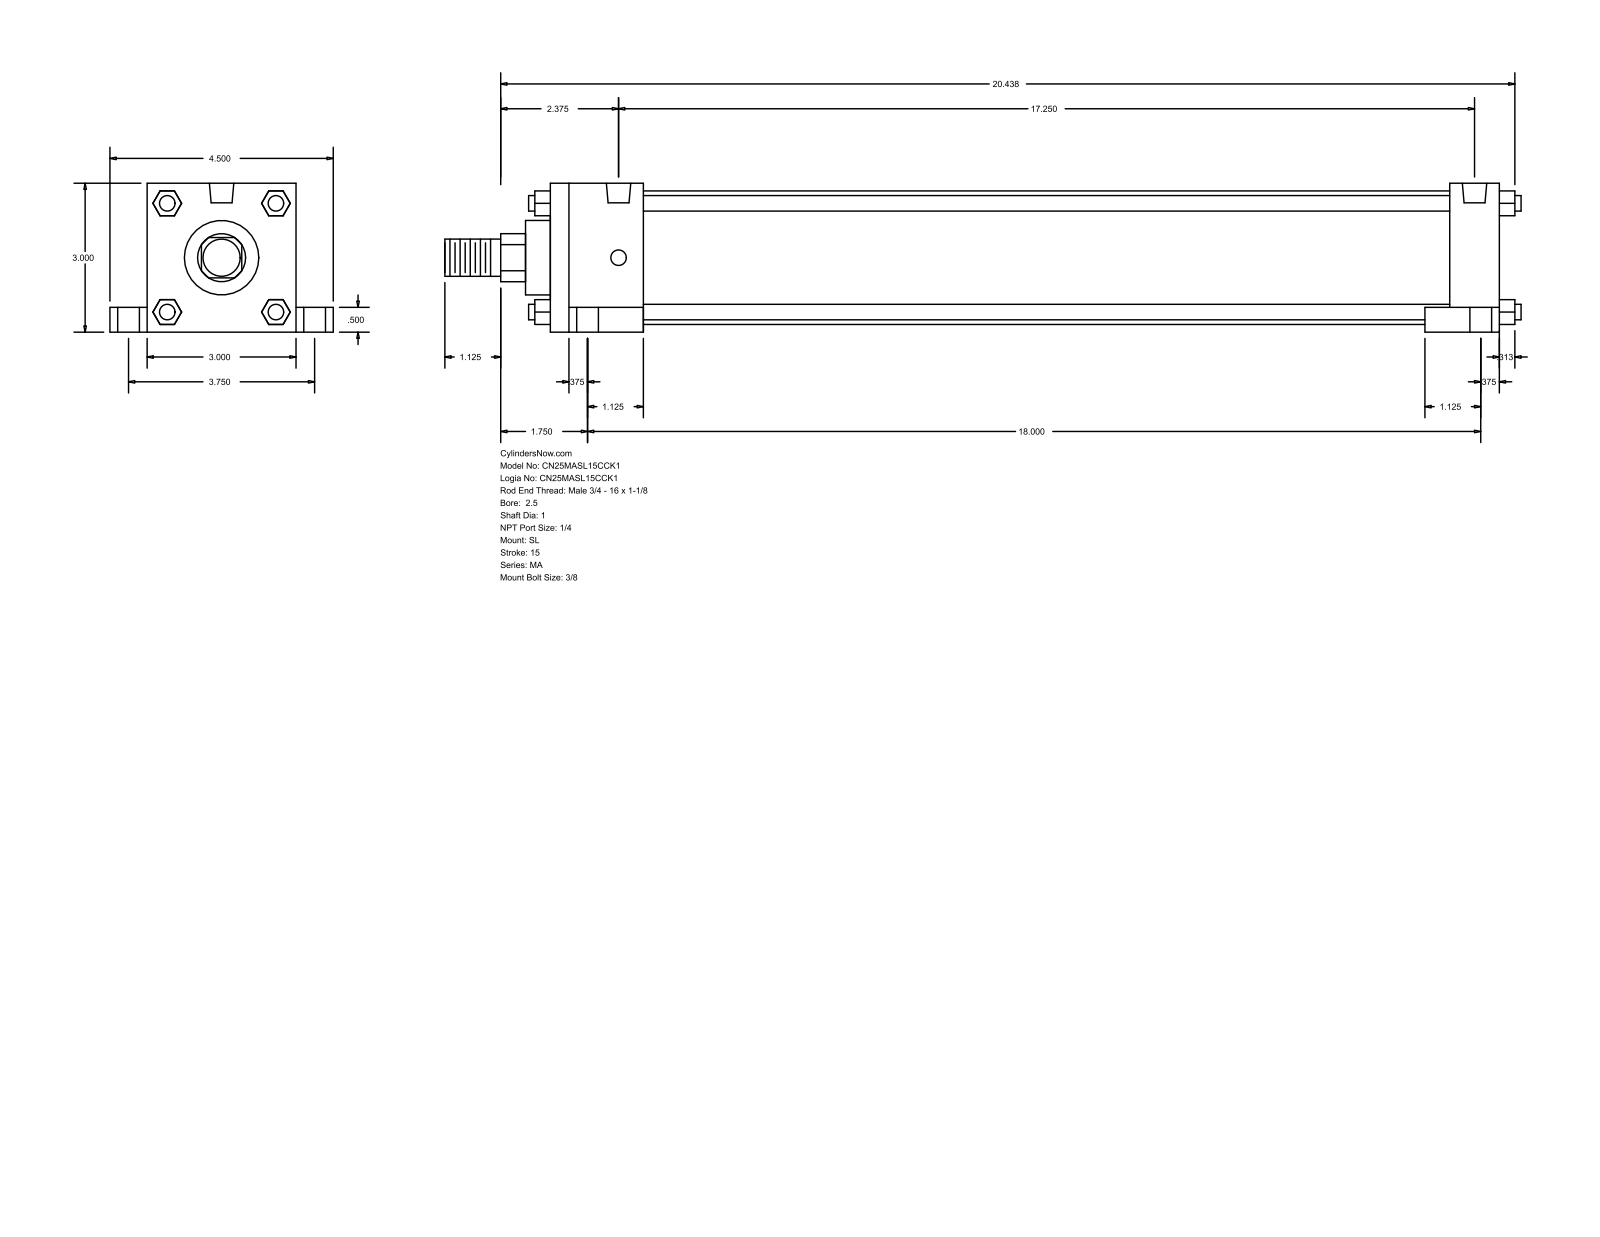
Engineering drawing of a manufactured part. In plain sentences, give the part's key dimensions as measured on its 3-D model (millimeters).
The part is named "MA_SL__0250_1". Its 3-D file was written by "GSSL Pune (CONFIG_CONTROL_DESIGN)". It is 0 solids with 148 faces: 112 planar, 36 cylindrical and 0 other. Overall it measures 550.86 by 114.3 by 76.2 millimeters. Round holes: 4 of diameter 7.94, 4 of diameter 11.11, 4 of diameter 17.46, 2 of diameter 12.49. Round bosses or shafts: 4 of diameter 7.94, 1 of diameter 68.33, 1 of diameter 38.1, 1 of diameter 25.4, 1 of diameter 19.05. Partial cylindrical surfaces (rounded edges, fillets, slot ends): 1 of radius 12.29. The main face-to-face distances are 76.2, 485.78, 12.7, 47.63, 438.15, 460.37, 412.74, 25.41, 19.05, 95.25. The hole center spacings are 47.73, 50.2, 95.24, 438.15, 443.88, 456.52, 457.2, 467.01.
